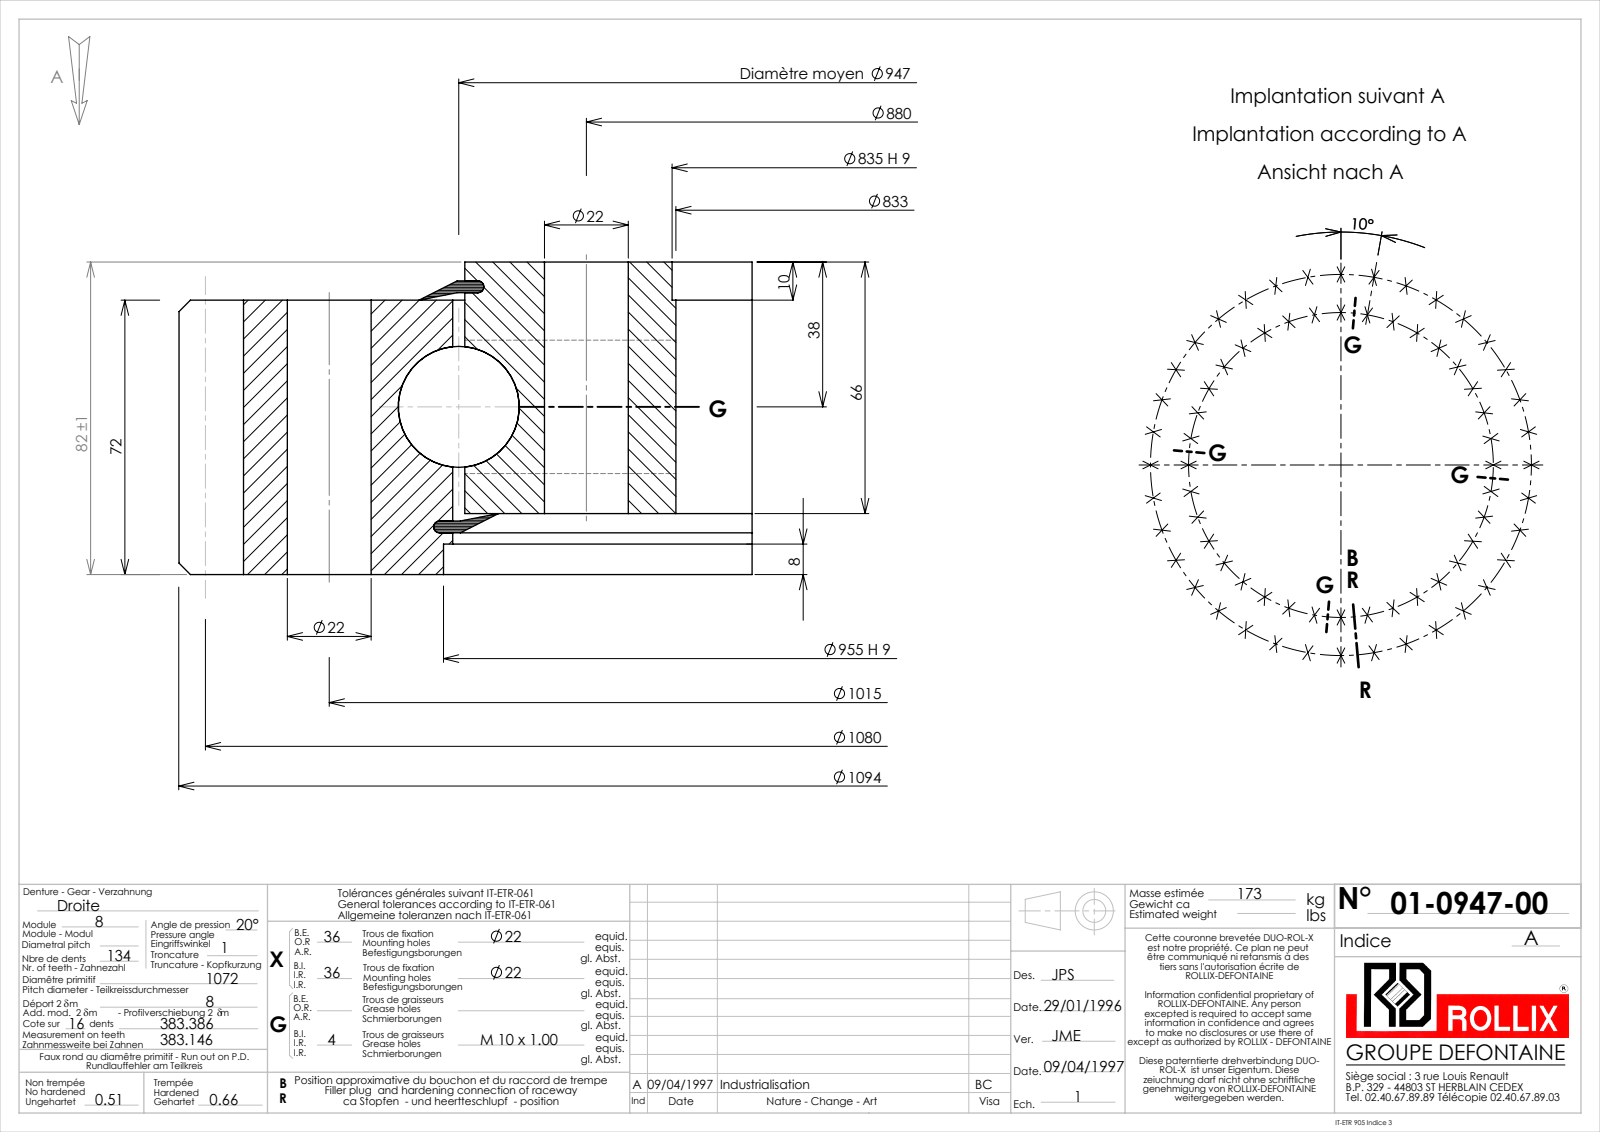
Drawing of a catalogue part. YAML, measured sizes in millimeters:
part_name: "01-0947-00"
step_written_by: "SolidWorks 2016 (CONFIG_CONTROL_DESIGN)"
units: millimeters
bodies: {solids: 5, faces: 1017, planar: 282, cylindrical: 439, other: 296}
overall_size: [1094, 1093.86, 82]
volume: 20990000
surface_area: 2388000
round_holes:
  - {diameter: 22, count: 72}
  - {diameter: 9, count: 4}
  - {diameter: 833, count: 1}
  - {diameter: 835, count: 1}
  - {diameter: 950.17, count: 1}
  - {diameter: 955, count: 1}
round_bosses_or_shafts:
  - {diameter: 943.83, count: 1}
partial_cylinders:
  - {radius: 530, count: 1}
  - {radius: 547, count: 1}
face_to_face_distances: [72, 16, 56, 82, 66, 10, 1.95, 57.95, 5.05, 61.05]
hole_center_spacings: [999.58, 347.15, 428.96, 652.43, 953.79, 1011.14, 919.9, 717.71]
